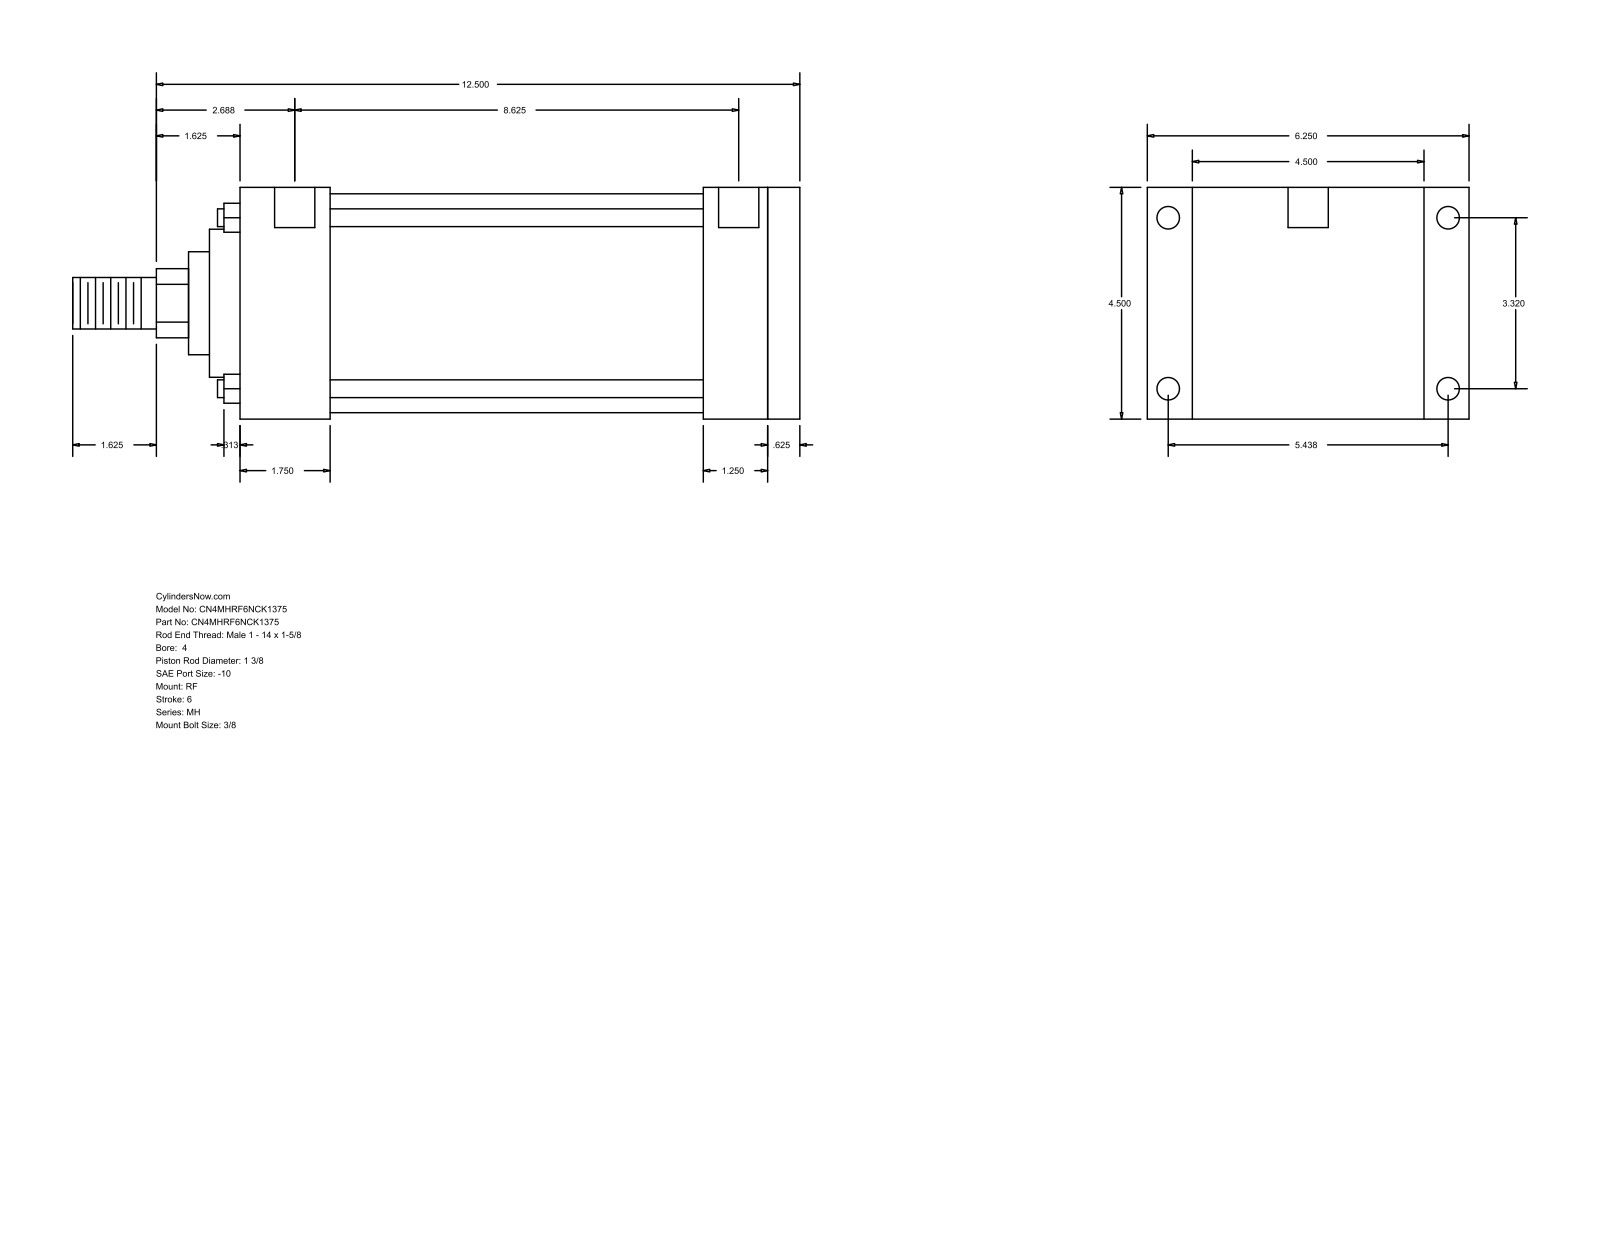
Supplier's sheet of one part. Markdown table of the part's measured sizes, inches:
| quantity | value |
| --- | --- |
| part name | MH_RF__0400_1.375 |
| STEP written by | GSSL Pune (CONFIG_CONTROL_DESIGN) |
| units | inches |
| bodies | 0 solids, 94 faces (65 planar, 29 cylindrical, 0 other) |
| overall size | 14.125 × 6.25 × 4.5 |
| round holes (diameter × count) | 0.344 × 4, 0.438 × 4, 0.781 × 2 |
| round bosses / shafts (diameter × count) | 0.345 × 4, 4.25 × 1, 2.875 × 1, 2 × 1, 1.375 × 1, 1 × 1 |
| partial cylindrical surfaces (radius × count) | 0.672 × 1 |
| main face-to-face distances | 4.5, 10.875, 0.625, 10.25, 1.75, 8.5, 9.125, 9, 7.25, 1.25 |
| hole center spacings | 0.063, 3.32, 5.438, 6.371, 8.688, 8.75, 8.625 |
